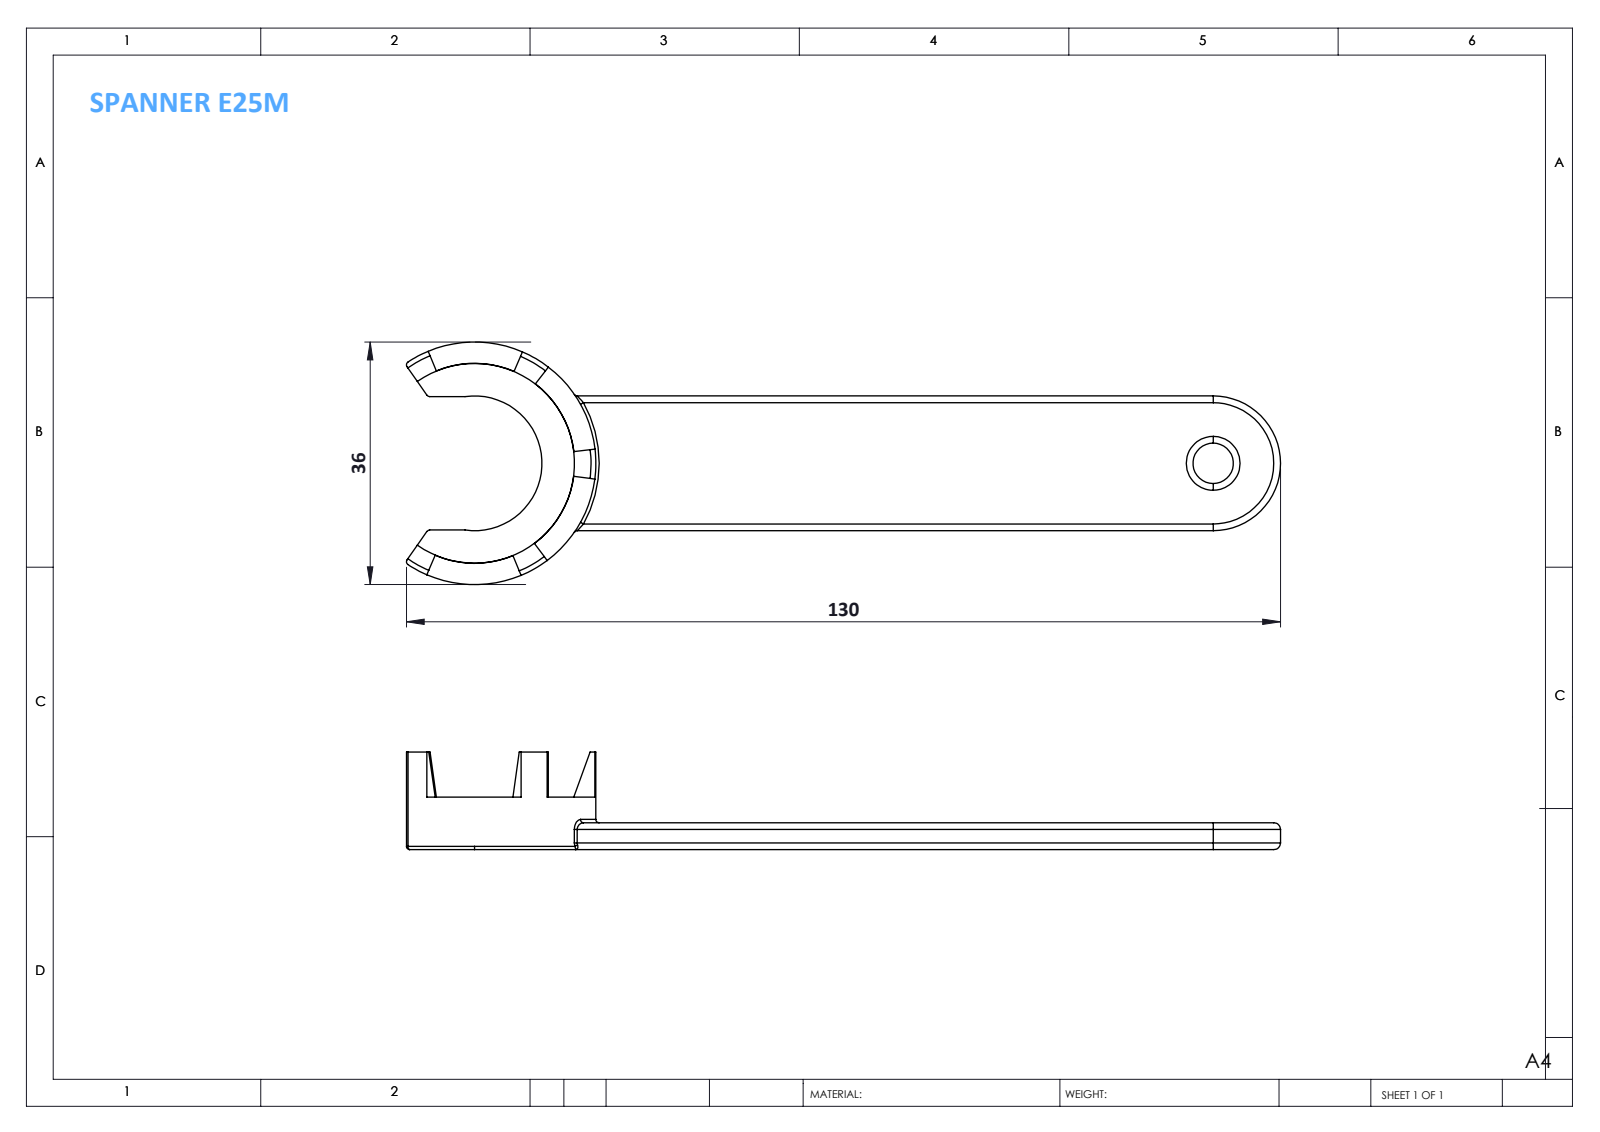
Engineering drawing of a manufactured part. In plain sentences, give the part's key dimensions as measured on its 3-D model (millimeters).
The part is named "SPANNER E25M". Its 3-D file was written by "SolidWorks 2014 (CONFIG_CONTROL_DESIGN)". It is 1 solid with 70 faces: 25 planar, 21 cylindrical and 24 other. Overall it measures 129.8 by 36 by 14.5 millimeters. Its volume is 11 151 cubic millimeters and its surface area 6 867 square millimeters. Round holes: 1 of diameter 6. Partial cylindrical surfaces (rounded edges, fillets, slot ends): 8 of radius 0.5, 4 of radius 1, 2 of radius 10, 1 of radius 18. The main face-to-face distances are 4, 20, 3.8, 7.8, 19.9, 19.8, 6.7, 10.5, 14.5.
